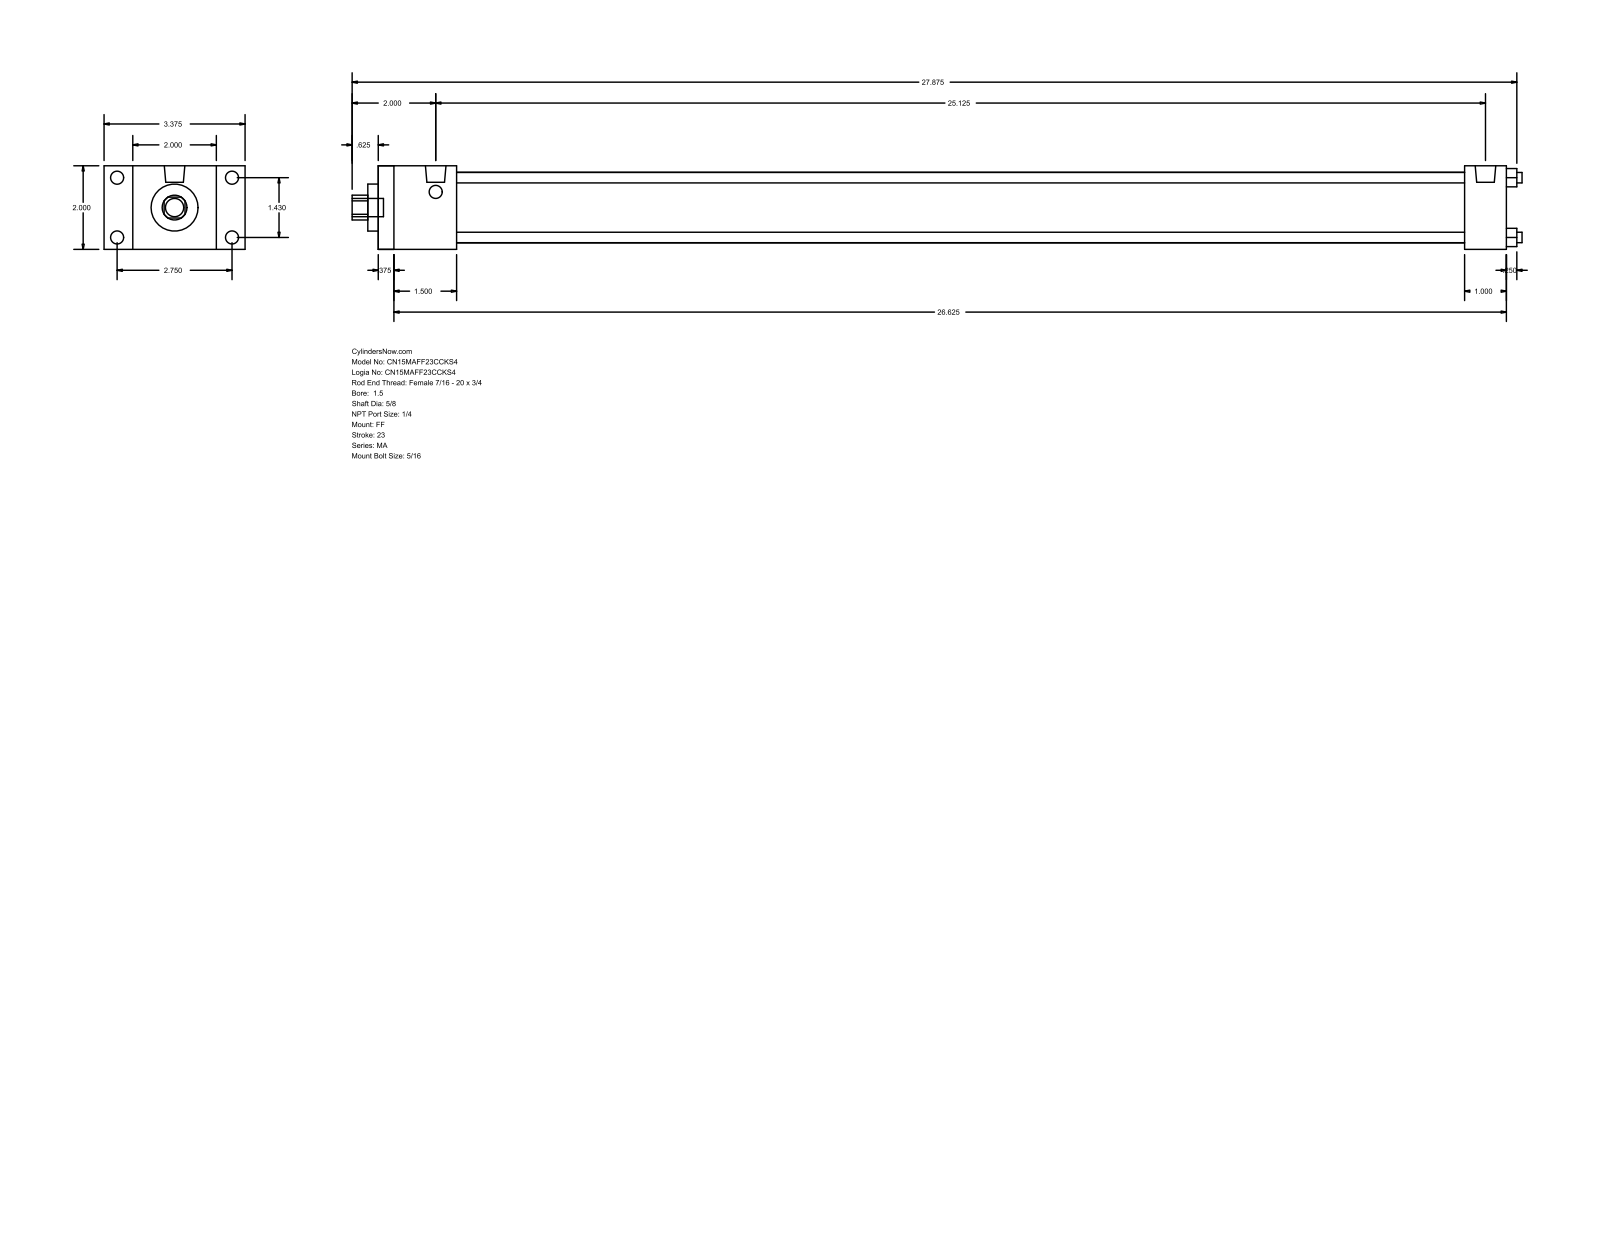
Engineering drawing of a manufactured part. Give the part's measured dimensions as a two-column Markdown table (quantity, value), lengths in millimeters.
| quantity | value |
| --- | --- |
| part name | MA_FF__0150_0.625 |
| STEP written by | GSSL Pune (CONFIG_CONTROL_DESIGN) |
| units | millimeters |
| bodies | 0 solids, 92 faces (64 planar, 28 cylindrical, 0 other) |
| overall size | 711.2 × 85.72 × 50.8 |
| round holes (diameter × count) | 6.35 × 4, 15.88 × 1, 28.57 × 1, 42.93 × 1 |
| round bosses / shafts (diameter × count) | 7.94 × 8, 12.49 × 2, 11.11 × 1 |
| partial cylindrical surfaces (radius × count) | 7.54 × 1 |
| main face-to-face distances | 50.8, 685.79, 9.52, 676.27, 25.4, 47.62, 660.39, 38.1, 650.87, 612.77 |
| hole center spacings | 25.68, 36.32, 51.36 |
